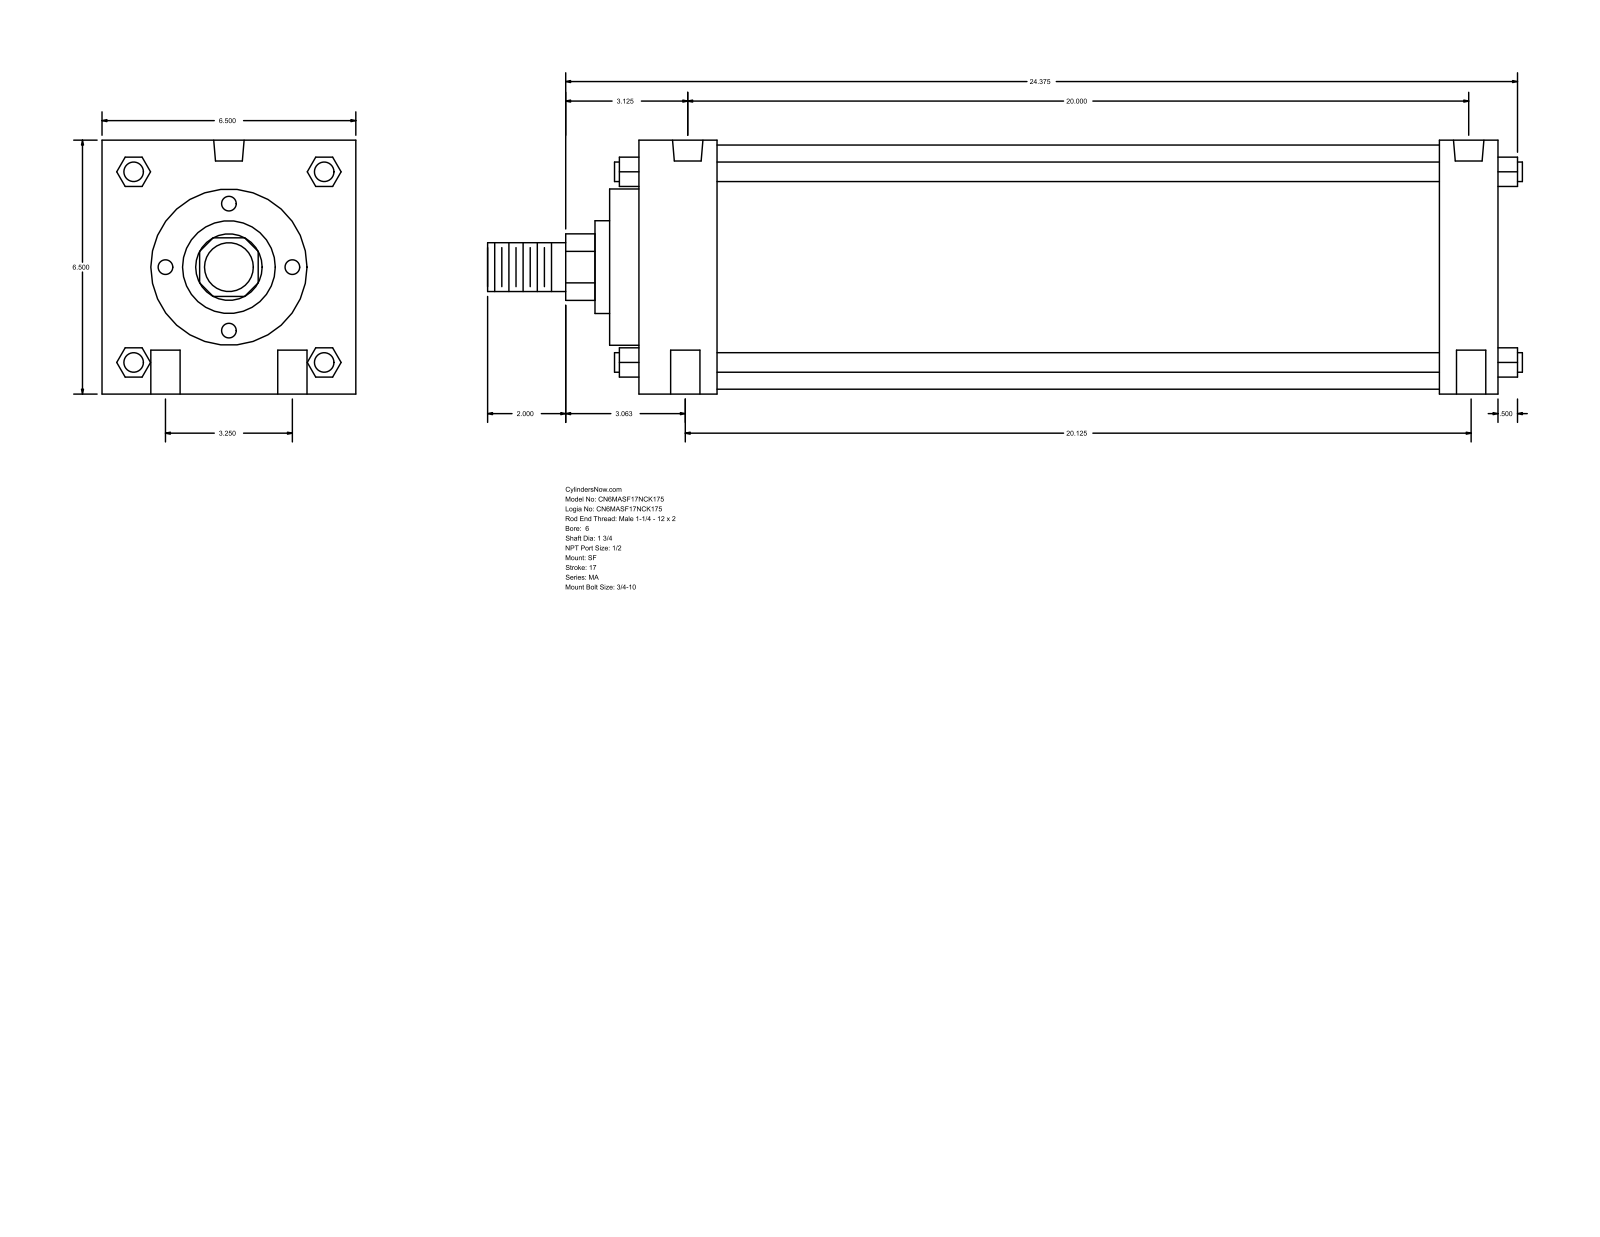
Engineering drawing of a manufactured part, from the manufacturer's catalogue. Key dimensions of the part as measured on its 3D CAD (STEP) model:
Part name (STEP PRODUCT): MA_SF__0600_1.75
STEP written by: GSSL Pune (CONFIG_CONTROL_DESIGN)
Units: millimetres
Bodies: 0 solids, 126 faces (95 planar, 31 cylindrical, 0 other)
Overall size (bounding box): 673.1 × 165.1 × 165.1
Round holes (diameter × count): ⌀19.05 ×4, ⌀17.46 ×2, ⌀19.77 ×2
Round bosses / shafts (diameter × count): ⌀12.7 ×4, ⌀158.75 ×1, ⌀101.6 ×1, ⌀60.33 ×1, ⌀44.45 ×1, ⌀31.75 ×1
Partial cylindrical surfaces — rounded edges, fillets, slot ends (radius × count): R21.63 ×1
Main face-to-face distances: 165.1, 558.8, 19.05, 50.8, 520.71, 38.09, 469.91, 508, 69.85, 539.76
Hole centre spacings: 41.3, 82.54, 508, 511.17, 511.25, 511.26, 517.79
